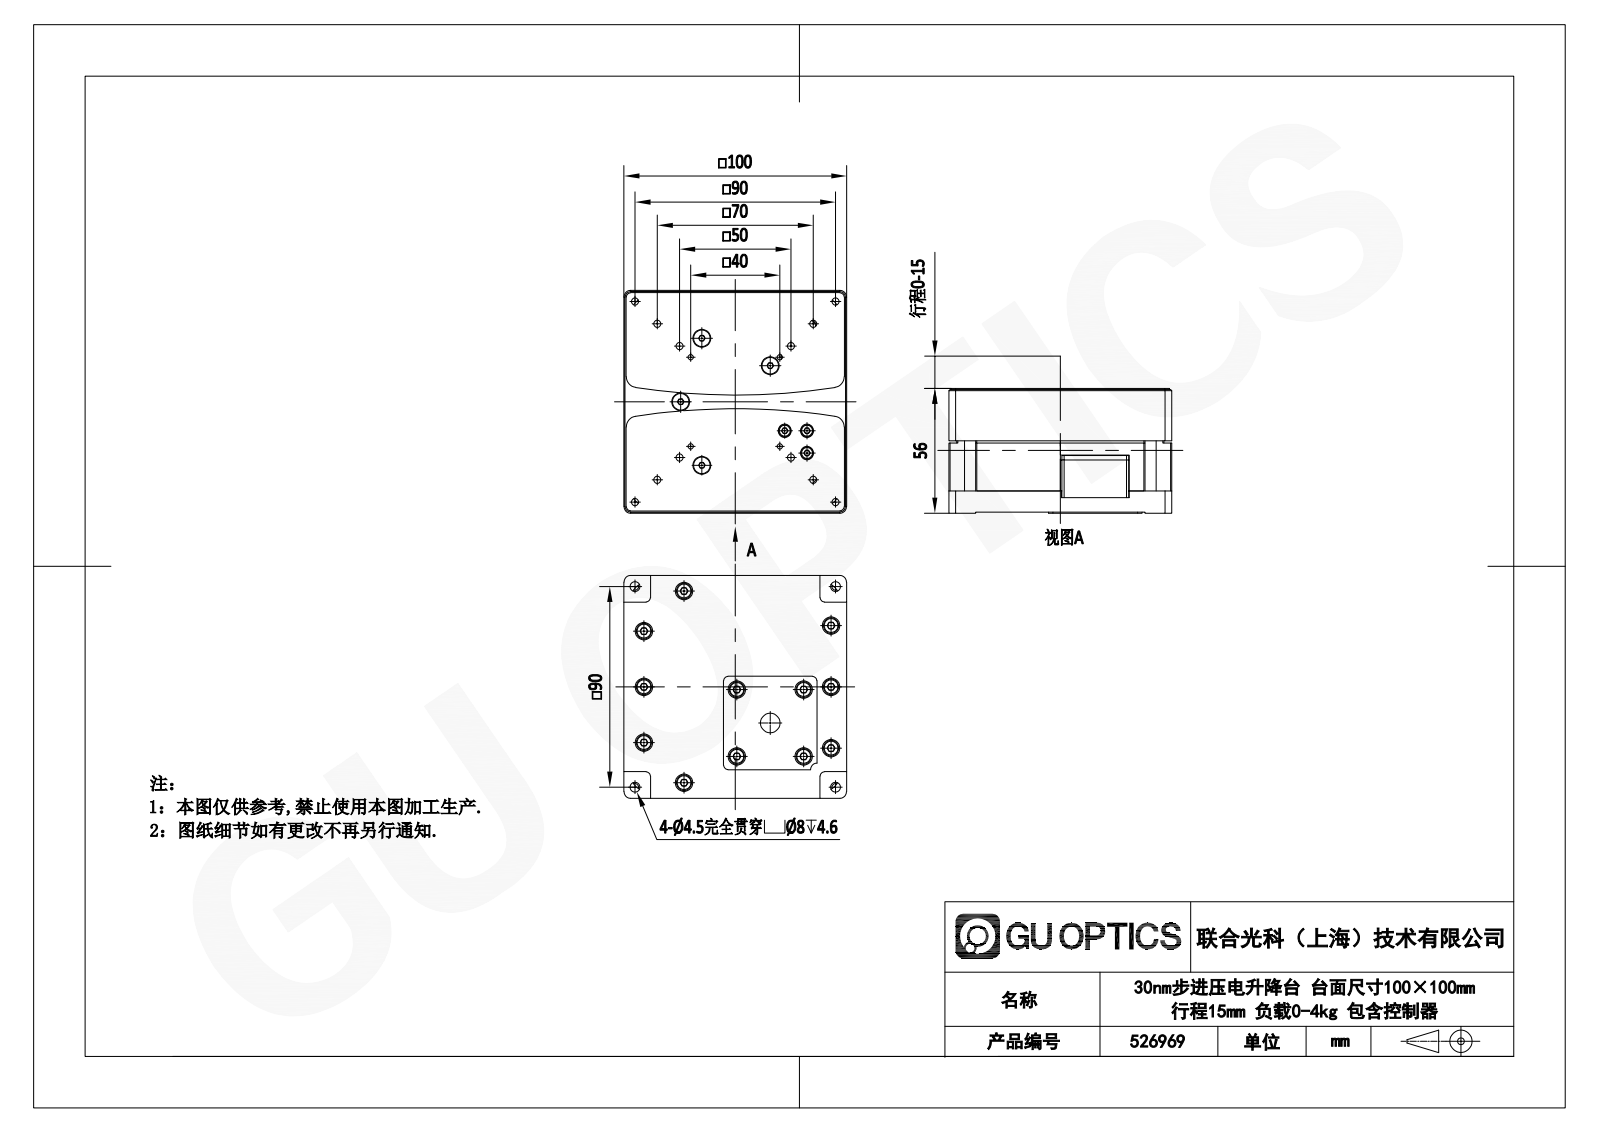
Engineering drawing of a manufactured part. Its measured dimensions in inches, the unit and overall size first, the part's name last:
Units: inches
Overall size (bounding box): 3.937 × 3.937 × 2.205
Round holes (diameter × count): ⌀0.177 ×29, ⌀0.13 ×20, ⌀0.315 ×20, ⌀0.098 ×11, ⌀0.094 ×4, ⌀0.106 ×4, ⌀0.118 ×4, ⌀0.169 ×4, ⌀0.323 ×4, ⌀0.063 ×3, ⌀0.1 ×3, ⌀0.134 ×3
Round bosses / shafts (diameter × count): ⌀0.157 ×19, ⌀0.276 ×15, ⌀0.296 ×4, ⌀0.217 ×3, ⌀0.118 ×3, ⌀0.15 ×2, ⌀0.079 ×2, ⌀0.352 ×1
Partial cylindrical surfaces — rounded edges, fillets, slot ends (radius × count): R0.079 ×44, R0.008 ×24, R0.118 ×17, R0.02 ×13, R0.039 ×13, R0.031 ×8, R0.059 ×8, R0.197 ×8
Main face-to-face distances: 0.374, 0.118, 0.335, 1.85, 1.811, 0.02, 3.937, 2.185, 0.256, 1.476
Hole centre spacings: 3.174, 0.835, 1.181, 0.557, 0.984, 0.568, 2.244, 2.742
Volume: 21.8 in³ · Surface area: 194.5 in²
Bodies: 30 solids, 2057 faces (1089 planar, 577 cylindrical, 391 other)
Part name (STEP PRODUCT): 526965; socket csink head cap screw 10642_din_EN ISO 10642 - M4 x 8 - 8N; socket head cap screw 4762_din_EN ISO 4762 M3 x 5 - 5N; ATOM (+2 more)
STEP written by: SolidWorks 2020 (CONFIG_CONTROL_DESIGN)
